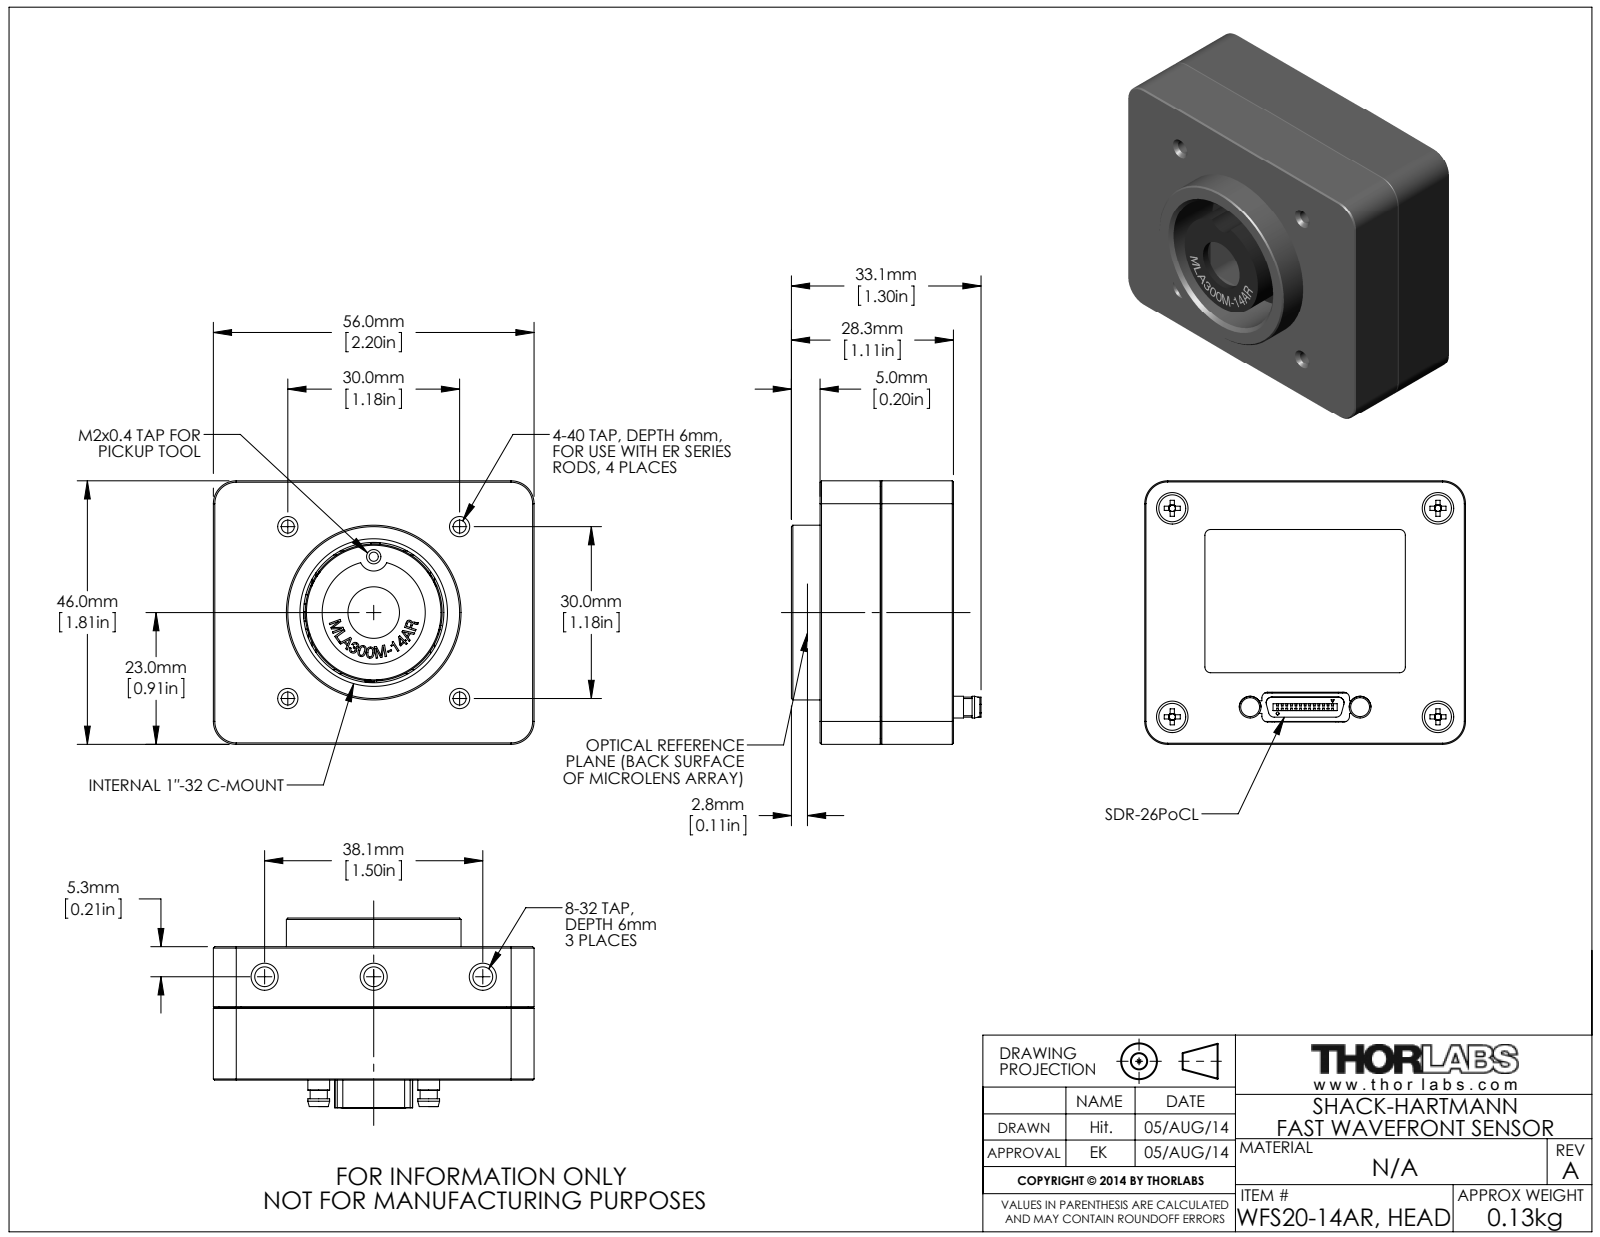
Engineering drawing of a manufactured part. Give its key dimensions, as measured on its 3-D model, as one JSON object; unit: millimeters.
{"part_name": "Halter Teil3 Typ300-14AR; Halter Teil2 Baugruppe; Kugel 2mm; Kamera aus GMK975-002_R023 (+8 more)", "step_written_by": "SolidWorks 2014 (AUTOMOTIVE_DESIGN)", "units": "millimeters", "bodies": {"solids": 51, "faces": 2481, "planar": 1189, "cylindrical": 698, "other": 594}, "overall_size": [56, 46, 33.11], "volume_mm3": 72732, "surface_area_mm2": 45165, "round_holes": [[0.6, 26], [3.2, 6], [2.05, 4], [2.26, 4], [2.7, 4], [2.9, 4], [3, 4], [6, 4], [1.9, 3], [3.45, 3], [1.2, 2], [1.75, 2]], "round_bosses_or_shafts": [[0.7, 108], [1, 11], [3, 8], [5.6, 4], [4.7, 4], [2.5, 4], [2.1, 4], [3.8, 2]], "partial_cylinders_radius": [[1, 19], [2, 12], [0.18, 6], [0.2, 4], [1.5, 4], [2.75, 4], [3.1, 4], [3.5, 4]], "face_to_face_distances": [14.98, 1.61, 16.59, 3.5, 19.39, 3.9, 13.5, 1.48, 3.09, 5.89], "hole_center_spacings": [1.4, 1.6, 2.66, 5.72, 3.2, 3.5, 4.16, 4.46]}
